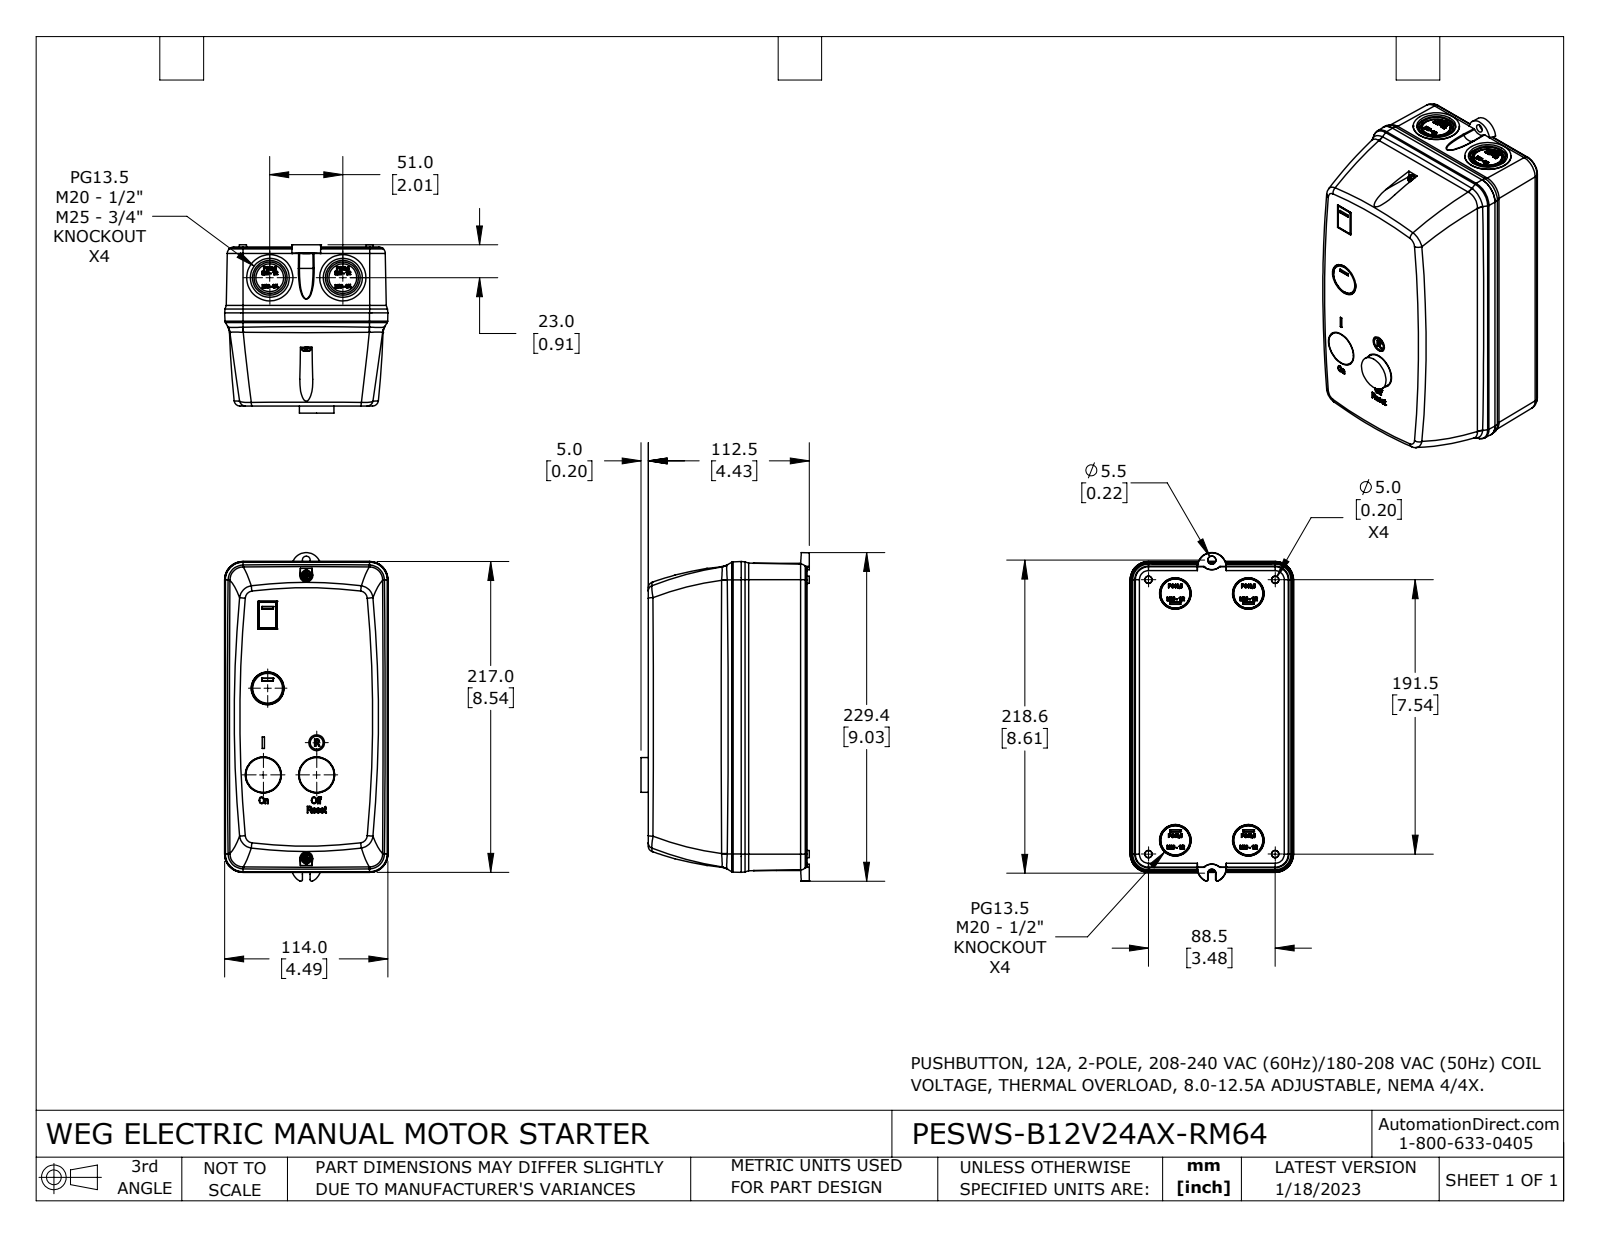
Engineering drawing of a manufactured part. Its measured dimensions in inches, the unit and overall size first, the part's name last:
Units: inches
Overall size (bounding box): 9.033 × 4.626 × 4.489
Round holes (diameter × count): ⌀0.173 ×2, ⌀0.863 ×2, ⌀1.072 ×2, ⌀0.217 ×1, ⌀0.433 ×1
Round bosses / shafts (diameter × count): ⌀1.27 ×2, ⌀0.955 ×2, ⌀0.953 ×2, ⌀0.763 ×2, ⌀0.276 ×2, ⌀0.118 ×2, ⌀0.354 ×1
Partial cylindrical surfaces — rounded edges, fillets, slot ends (radius × count): R0.079 ×4, R0.181 ×4, R0.376 ×4, R0.257 ×2, R0.297 ×2, R0.082 ×1, R0.085 ×1, R0.108 ×1
Main face-to-face distances: 1.811, 2.559, 4.37, 0.02, 4.35, 1.791, 4.331, 0.039, 4.311, 2.52
Hole centre spacings: 0.413, 2.008, 3.202, 4.615, 5.028, 7.795, 8.209
Volume: 149.9 in³ · Surface area: 257.6 in²
Bodies: 6 solids, 2195 faces (1110 planar, 92 cylindrical, 993 other)
Part name (STEP PRODUCT): PESWS-B12V24AX-RM64
STEP written by: SolidWorks 2021 (CONFIG_CONTROL_DESIGN)
